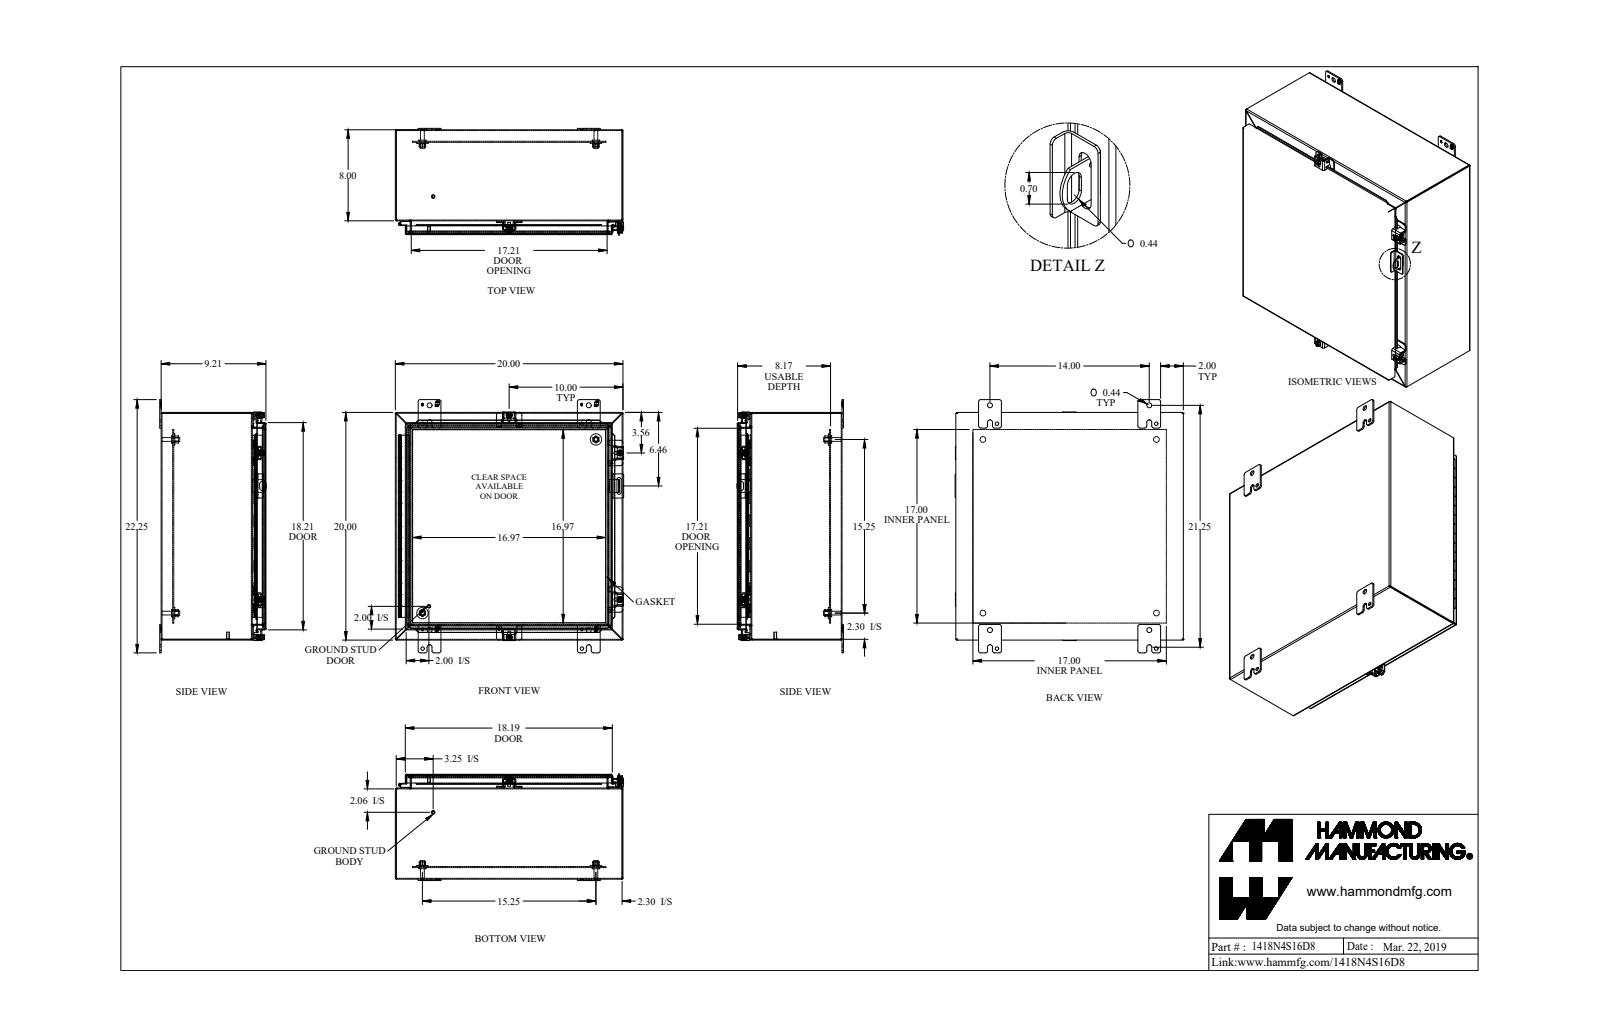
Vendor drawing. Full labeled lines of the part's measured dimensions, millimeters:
Part name (STEP PRODUCT): 1418N4S16D8_Default
STEP written by: SolidWorks 2019 (CONFIG_CONTROL_DESIGN)
Units: millimetres
Bodies: 39 solids, 1329 faces (728 planar, 467 cylindrical, 134 other)
Overall size (bounding box): 565.2 × 509.6 × 238.1
Volume: 2 566 000 mm³ · Surface area: 2 674 000 mm²
Round holes (diameter × count): ⌀5.4 ×4, ⌀6.7 ×4, ⌀8 ×4, ⌀9.5 ×4, ⌀11.1 ×4, ⌀12.7 ×4, ⌀7.8 ×2, ⌀11.3 ×2, ⌀2.8 ×1, ⌀3.2 ×1
Round bosses / shafts (diameter × count): ⌀16.5 ×4, ⌀12.7 ×4, ⌀9.9 ×4, ⌀9.5 ×4, ⌀8.4 ×4, ⌀6.2 ×4, ⌀25.4 ×2, ⌀8 ×2
Partial cylindrical surfaces — rounded edges, fillets, slot ends (radius × count): R4.8 ×26, R0.9 ×24, R2.7 ×24, R1.2 ×21, R3.6 ×21, R6.4 ×20, R3.2 ×10, R1.1 ×8
Main face-to-face distances: 1.8, 506.2, 230.3, 232.1, 232.1, 1.8, 233.9, 23.8, 504.3, 508
Hole centre spacings: 387.4, 201.1, 355.6, 482, 564.8, 61.8, 77.9, 425.8
